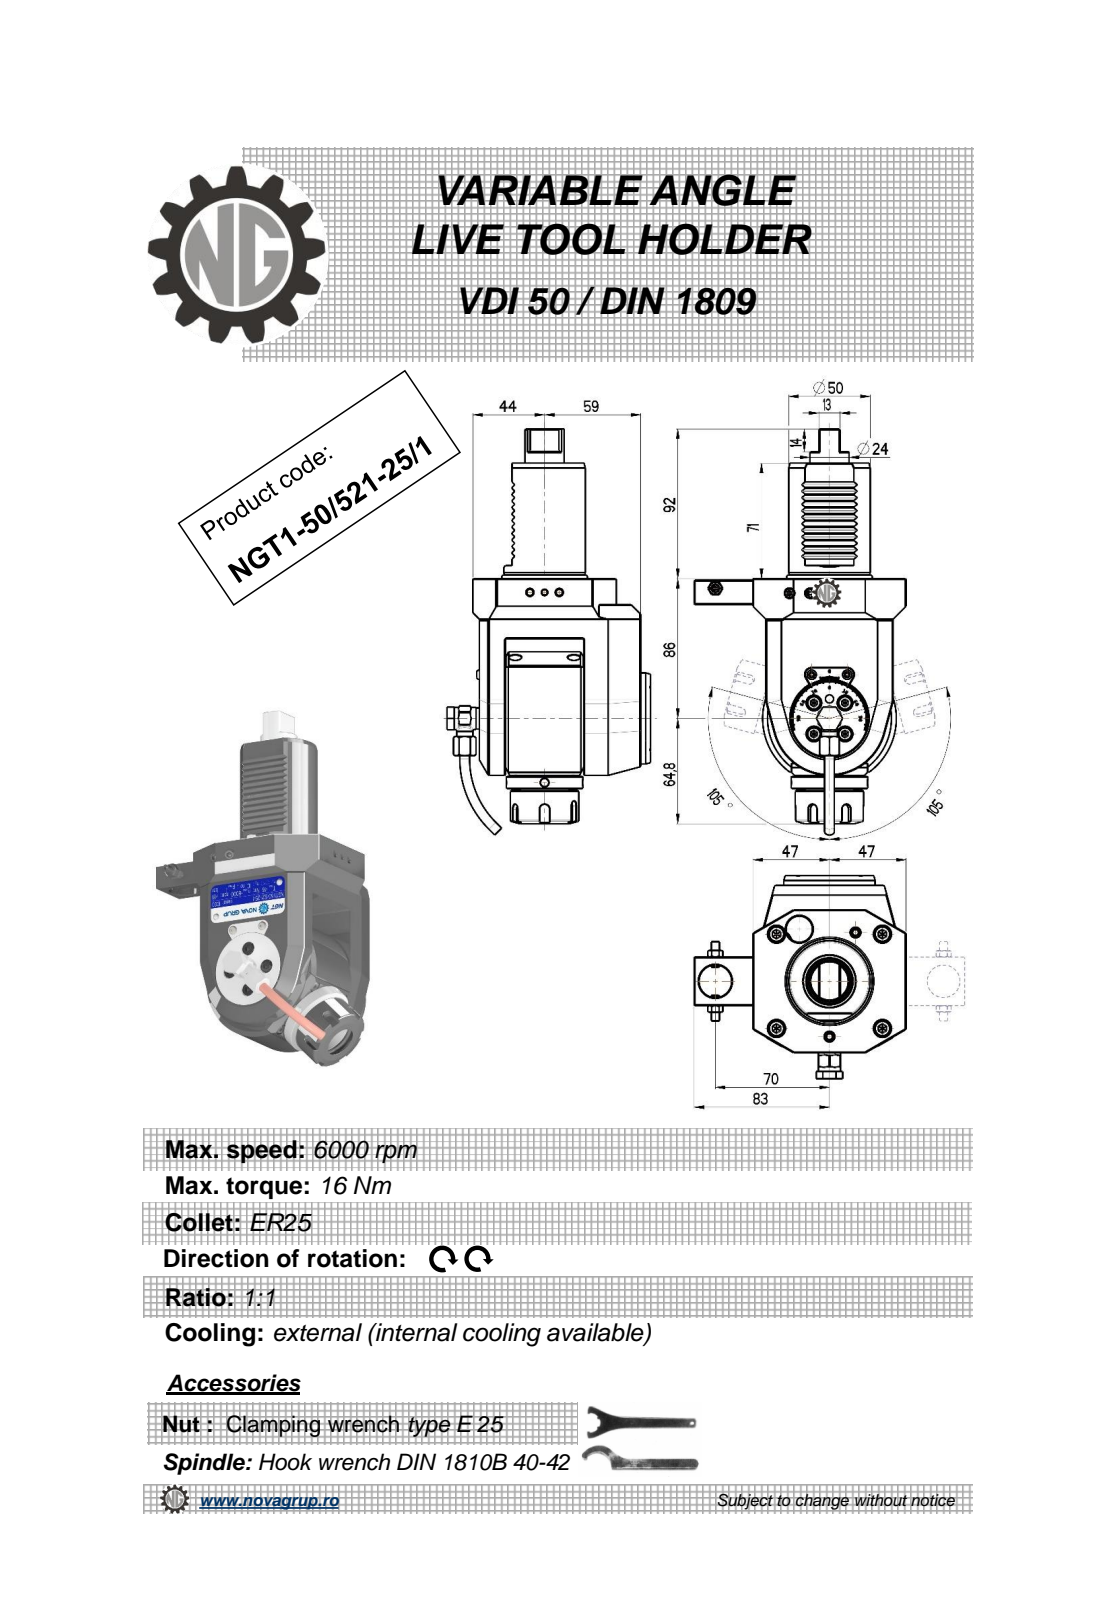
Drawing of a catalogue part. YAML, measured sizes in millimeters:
part_name: "NGT1_50_521_25_1"
step_written_by: "PRO/ENGINEER BY PARAMETRIC TECHNOLOGY CORPORATION, 2010280 (CONFIG_CONTROL_DESIGN)"
units: millimeters
bodies: {solids: 1, faces: 596, planar: 265, cylindrical: 138, other: 193}
overall_size: [249.67, 130, 124.9]
volume: 1015000
surface_area: 91406
round_holes:
  - {diameter: 4, count: 3}
  - {diameter: 5, count: 2}
  - {diameter: 3, count: 1}
  - {diameter: 6.2, count: 1}
  - {diameter: 9, count: 1}
  - {diameter: 9.5, count: 1}
  - {diameter: 10, count: 1}
  - {diameter: 11, count: 1}
  - {diameter: 20, count: 1}
  - {diameter: 20.3, count: 1}
round_bosses_or_shafts:
  - {diameter: 6, count: 2}
  - {diameter: 5.7, count: 2}
  - {diameter: 82, count: 1}
  - {diameter: 56, count: 1}
  - {diameter: 50, count: 1}
  - {diameter: 47, count: 1}
  - {diameter: 42, count: 1}
  - {diameter: 35, count: 1}
partial_cylinders:
  - {radius: 0.26, count: 12}
  - {radius: 0.3, count: 12}
  - {radius: 0.16, count: 6}
  - {radius: 3, count: 5}
  - {radius: 0.5, count: 4}
  - {radius: 0.8, count: 2}
  - {radius: 1, count: 2}
  - {radius: 10, count: 2}
face_to_face_distances: [37, 16, 99, 21, 8, 6, 64, 105, 20, 35]
hole_center_spacings: [0.4, 39.45, 49, 49.4, 70, 85.45, 85.68, 116.95]
